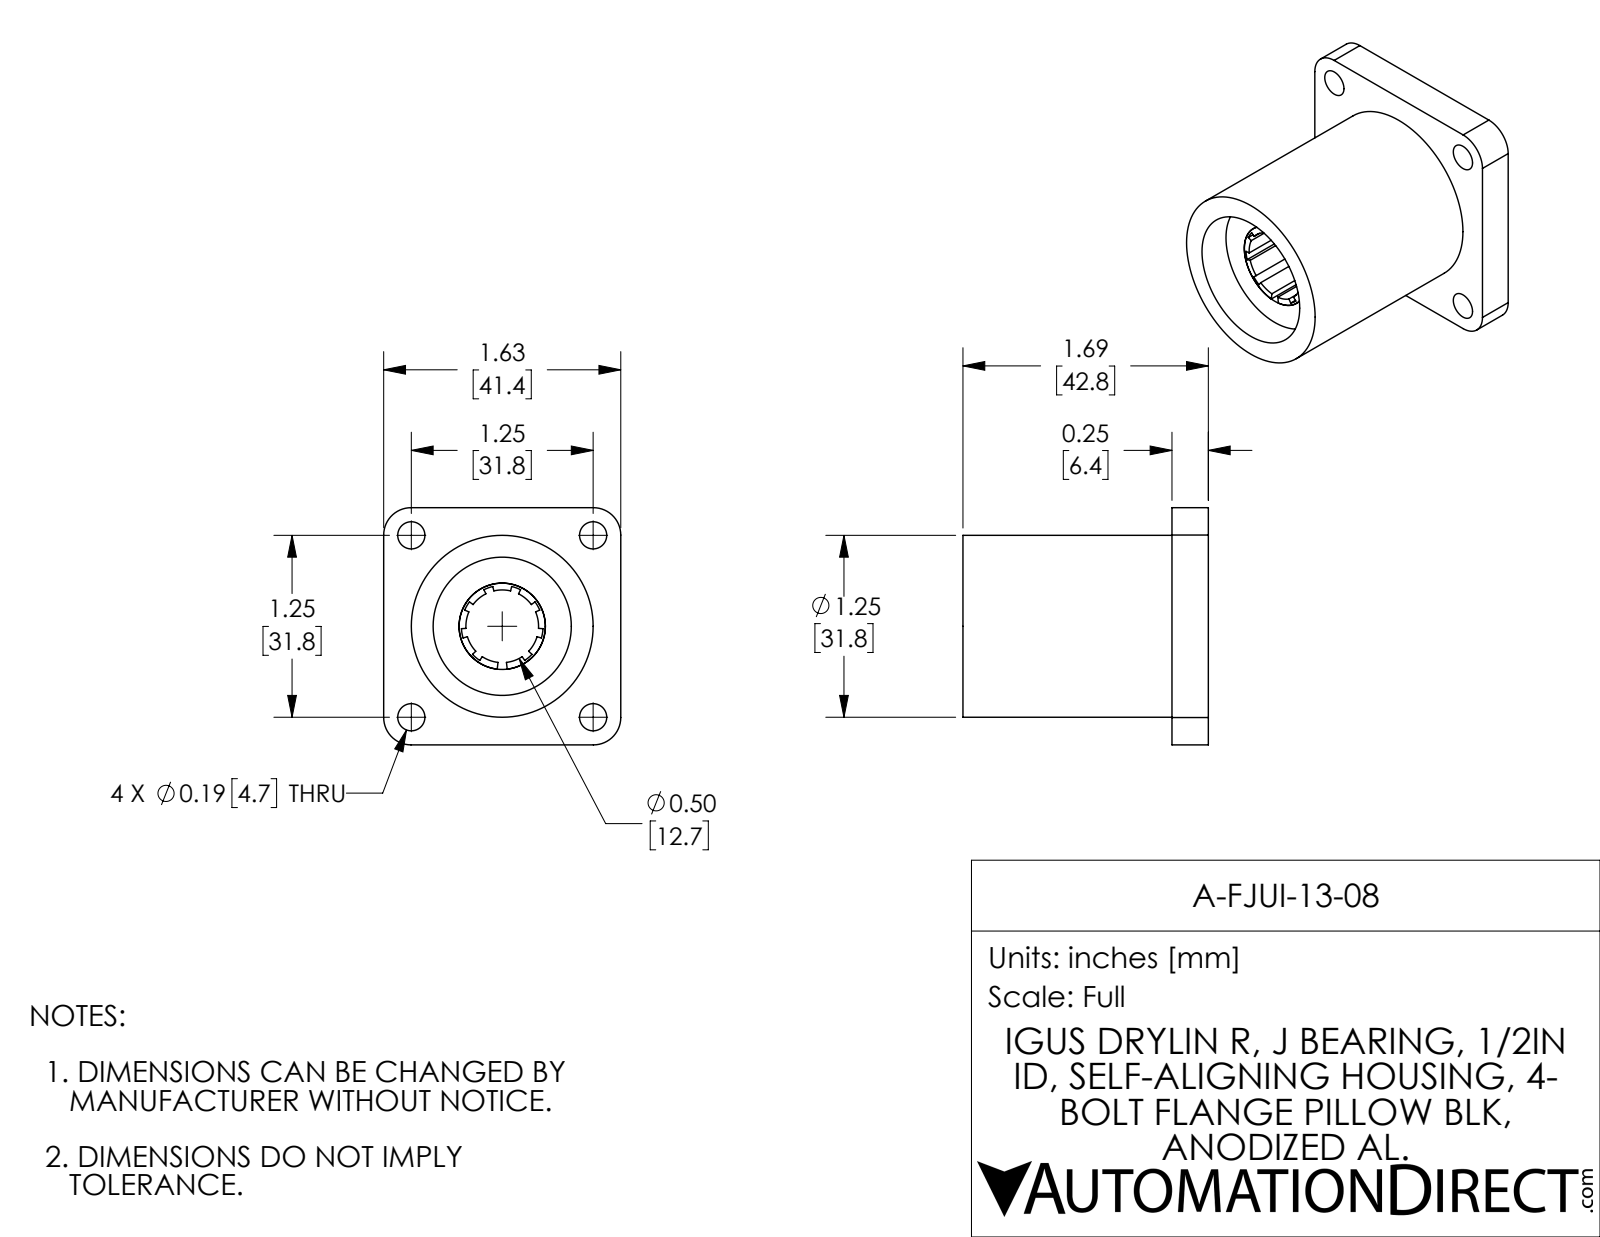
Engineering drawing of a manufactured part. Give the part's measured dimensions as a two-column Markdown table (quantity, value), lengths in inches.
| quantity | value |
| --- | --- |
| part name | A-FJUI-13-08 |
| STEP written by | SolidWorks 2017 (AUTOMOTIVE_DESIGN) |
| units | inches |
| bodies | 2 solids, 117 faces (64 planar, 53 cylindrical, 0 other) |
| overall size | 1.687 × 1.63 × 1.63 |
| volume | 1.806 in³ |
| surface area | 21.06 in² |
| round holes (diameter × count) | 0.187 × 4, 0.95 × 1 |
| round bosses / shafts (diameter × count) | 1.25 × 1, 0.593 × 1, 0.102 × 1 |
| partial cylindrical surfaces (radius × count) | 0.188 × 4, 0.25 × 1, 0.281 × 1, 0.328 × 1 |
| main face-to-face distances | 0.25, 1.63, 1.687, 1.437, 1.454, 1.204, 0.233, 0.233, 0.017, 1.22 |
| hole center spacings | 0.884, 1.25, 1.769 |
